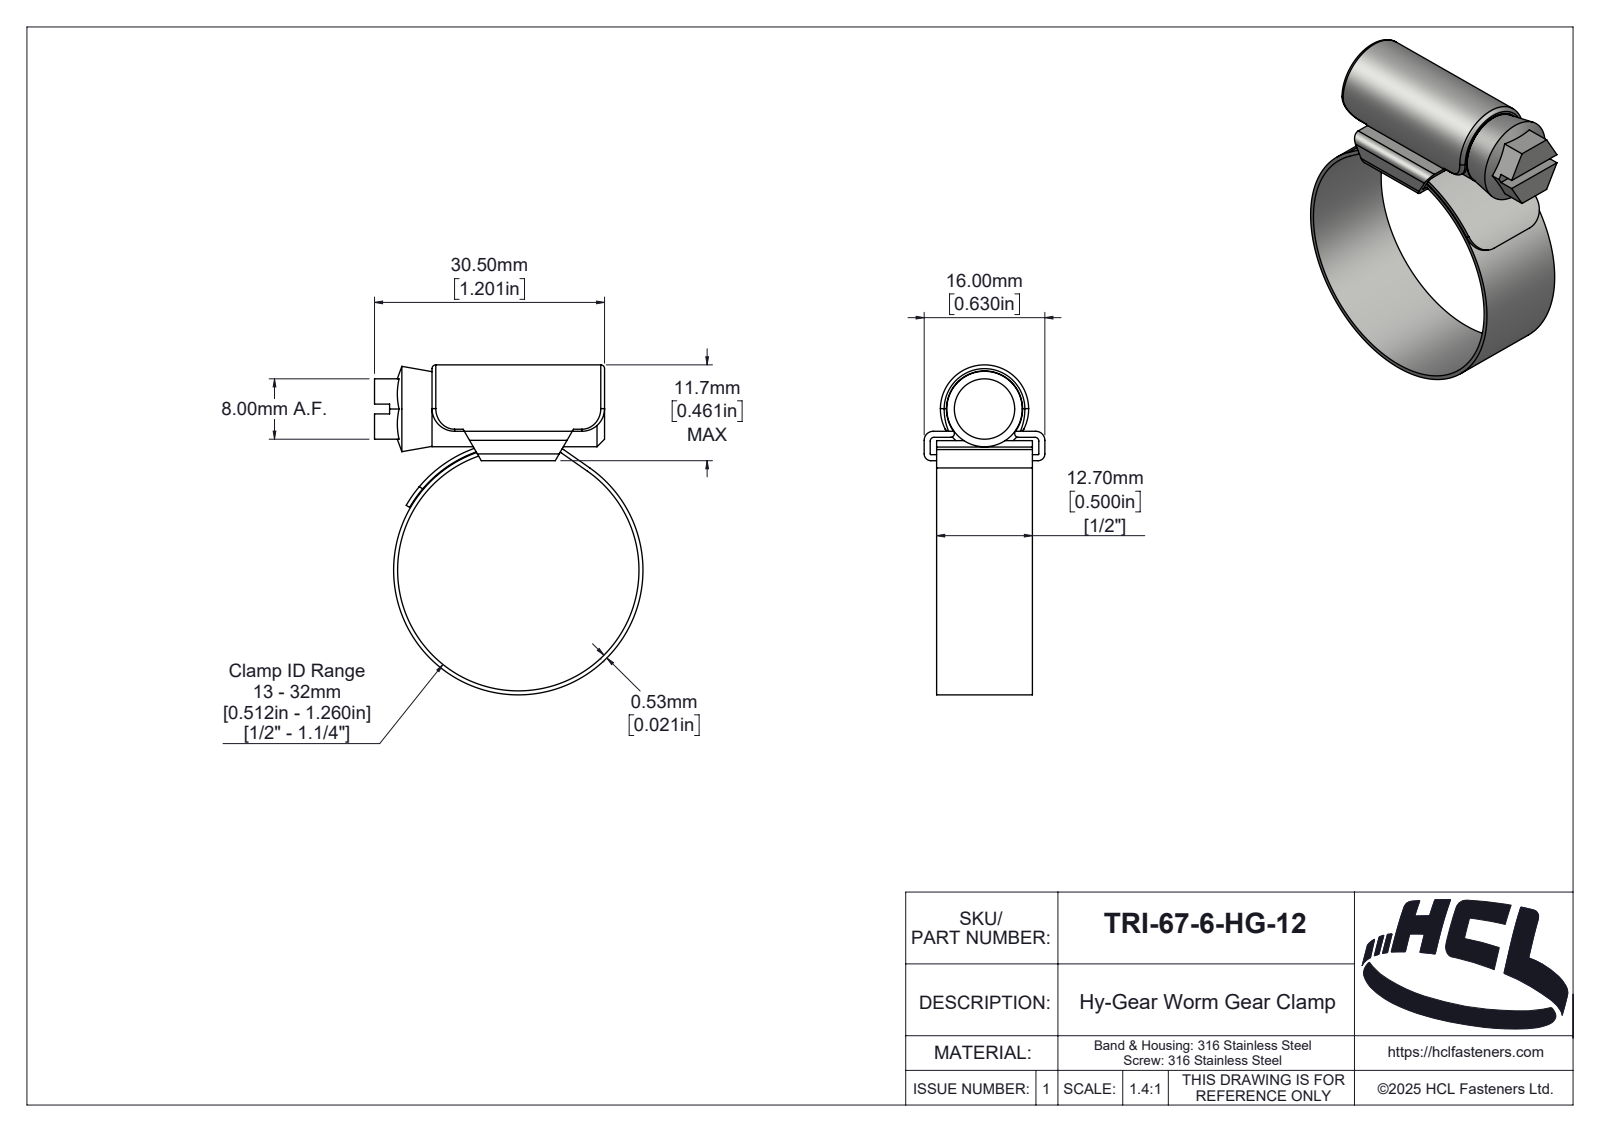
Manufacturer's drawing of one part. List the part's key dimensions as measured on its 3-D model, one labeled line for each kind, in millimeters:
Part name (STEP PRODUCT): TRI-57-0-HG-12
STEP written by: SolidWorks 2025 (AUTOMOTIVE_DESIGN)
Units: millimetres
Bodies: 3 solids, 189 faces (39 planar, 89 cylindrical, 61 other)
Overall size (bounding box): 43.73 × 35.59 × 16
Volume: 3 800 mm³ · Surface area: 6 084 mm²
Round holes (diameter × count): ⌀32 ×1
Round bosses / shafts (diameter × count): ⌀33.06 ×1, ⌀10 ×1
Partial cylindrical surfaces — rounded edges, fillets, slot ends (radius × count): R0.5 ×6, R3 ×4, R0.1 ×2, R0.9 ×2, R1.2 ×2, R0.46 ×1, R1.89 ×1, R2 ×1
Main face-to-face distances: 0.8, 3.1, 2.3, 12.7, 0.53, 3.9, 30.5, 1.65, 14.35, 15.2
